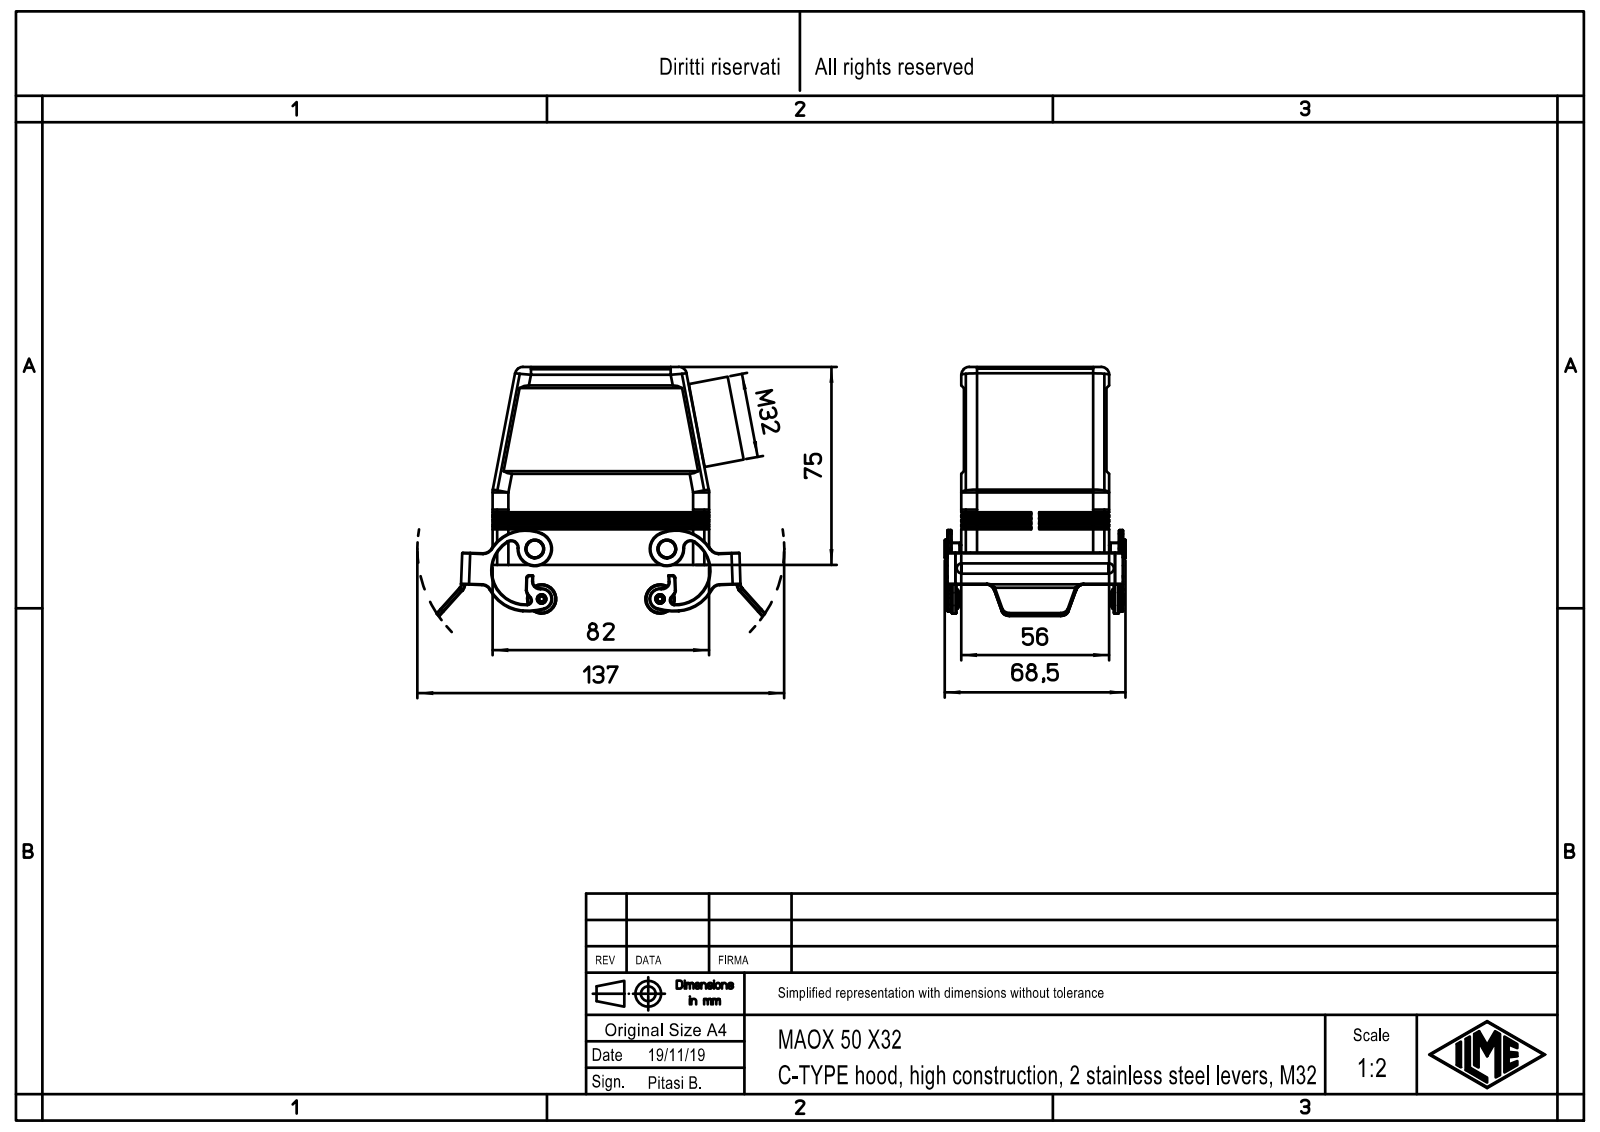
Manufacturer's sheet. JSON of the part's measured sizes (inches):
{"part_name": "MAOX 50 X32; MAOX 50 X32.stp", "step_written_by": "Creo Elements/Direct Modeling 20.1B 02-Apr-2019 (C) Parametric Technology GmbH (AUTOMOTIVE_DESIGN)", "units": "inches", "bodies": {"solids": 1, "faces": 706, "planar": 298, "cylindrical": 320, "other": 88}, "overall_size": [4.834, 3.766, 2.697], "volume_in3": 5.39, "surface_area_in2": 93.02, "round_holes": [[0.097, 8], [0.138, 8], [0.197, 4], [0.079, 2], [0.122, 2], [1.102, 1], [1.26, 1]], "round_bosses_or_shafts": [[0.276, 4], [0.189, 4], [0.433, 2], [0.138, 2], [0.118, 2], [1.535, 1]], "partial_cylinders_radius": [[0.118, 20], [0.01, 14], [0.079, 12], [0.236, 10], [0.059, 6], [0.138, 6], [0.217, 6], [0.098, 4]], "face_to_face_distances": [0.118, 2.087, 0.039, 1.969, 0.079, 2.165, 2.047, 0.325, 0.059, 2.205], "hole_center_spacings": [0.63, 0.945, 2.598, 2.674, 2.765, 0.315, 0.751, 1.575]}
